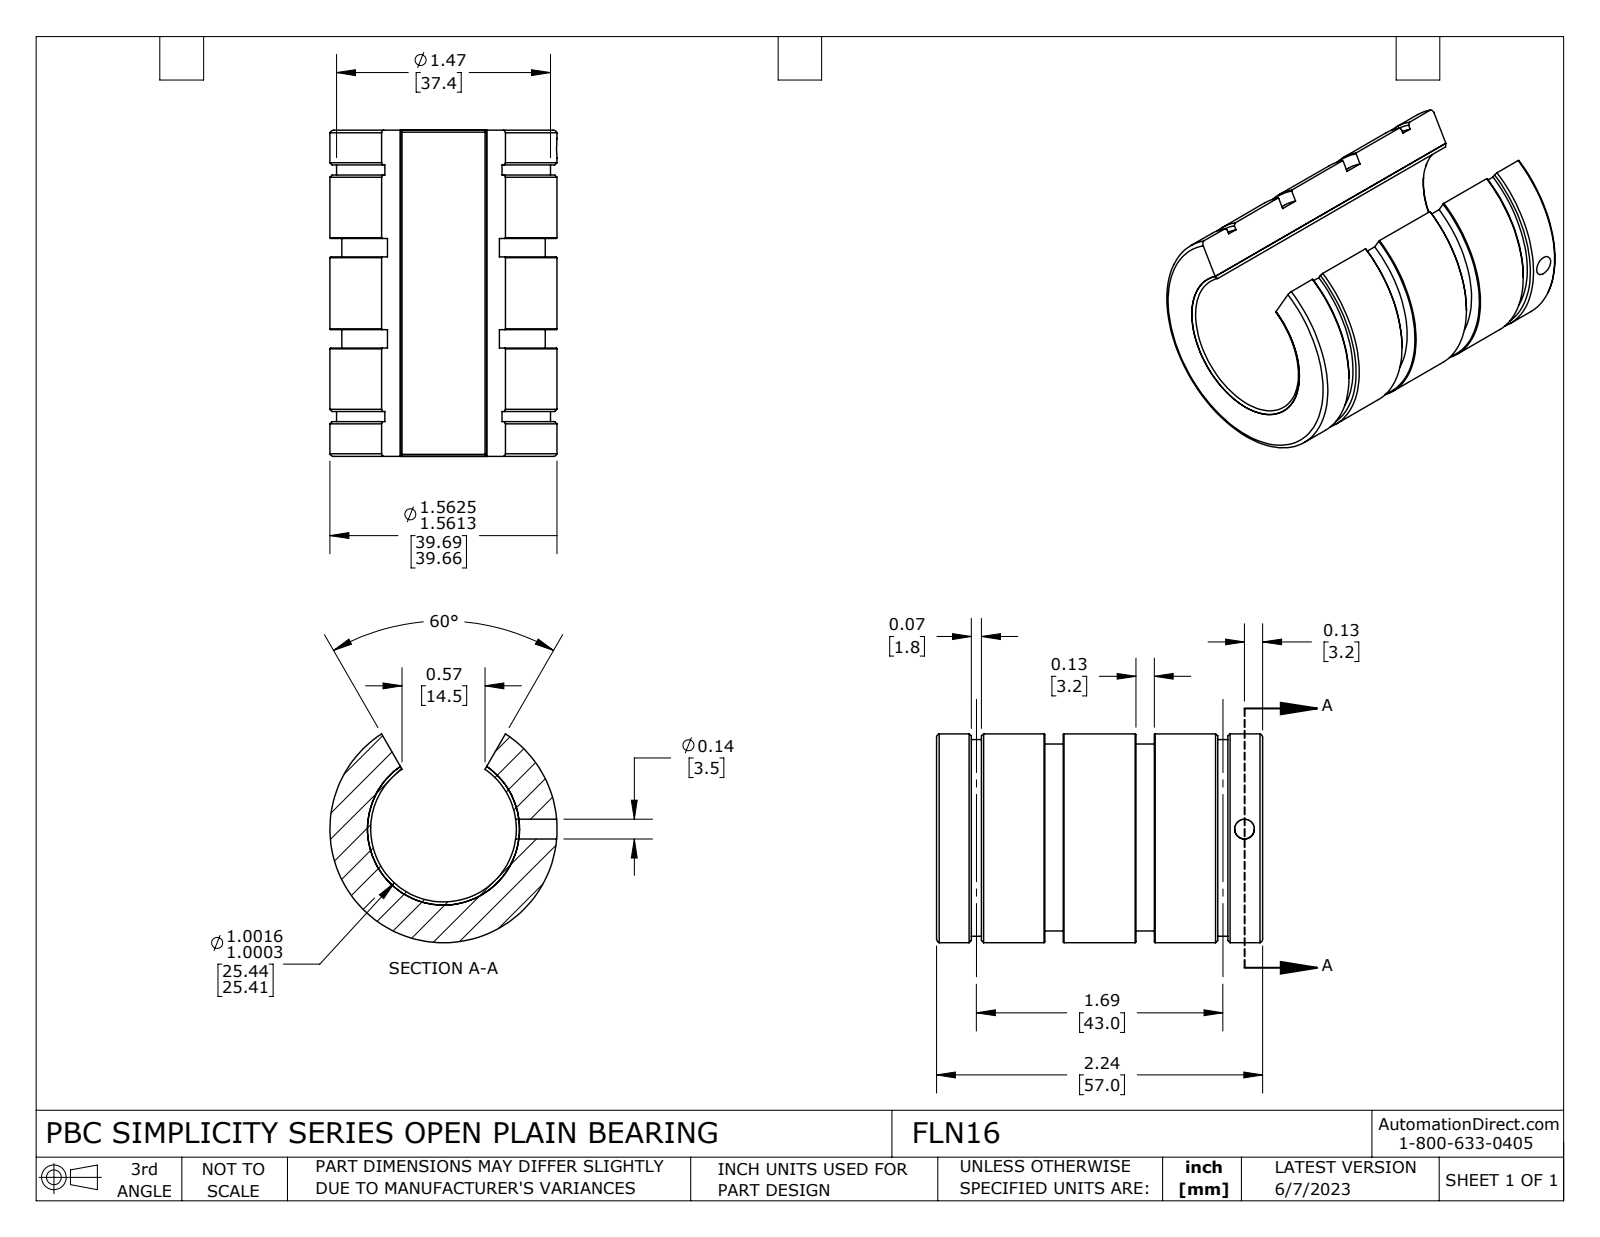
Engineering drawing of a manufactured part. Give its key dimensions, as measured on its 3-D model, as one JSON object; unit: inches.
{"part_name": "FLN16", "step_written_by": "SolidWorks 2021 (CONFIG_CONTROL_DESIGN)", "units": "inches", "bodies": {"solids": 2, "faces": 82, "planar": 14, "cylindrical": 40, "other": 28}, "overall_size": [2.243, 1.562, 1.435], "volume_in3": 1.946, "surface_area_in2": 31.13, "round_holes": [[0.136, 1], [1.001, 1], [1.045, 1]], "round_bosses_or_shafts": [[1.562, 1], [1.471, 1], [1.399, 1]], "face_to_face_distances": [2.243, 0.745, 1.497, 0.871, 1.371, 0.126, 0.626, 0.752, 0.5, 0.239]}
